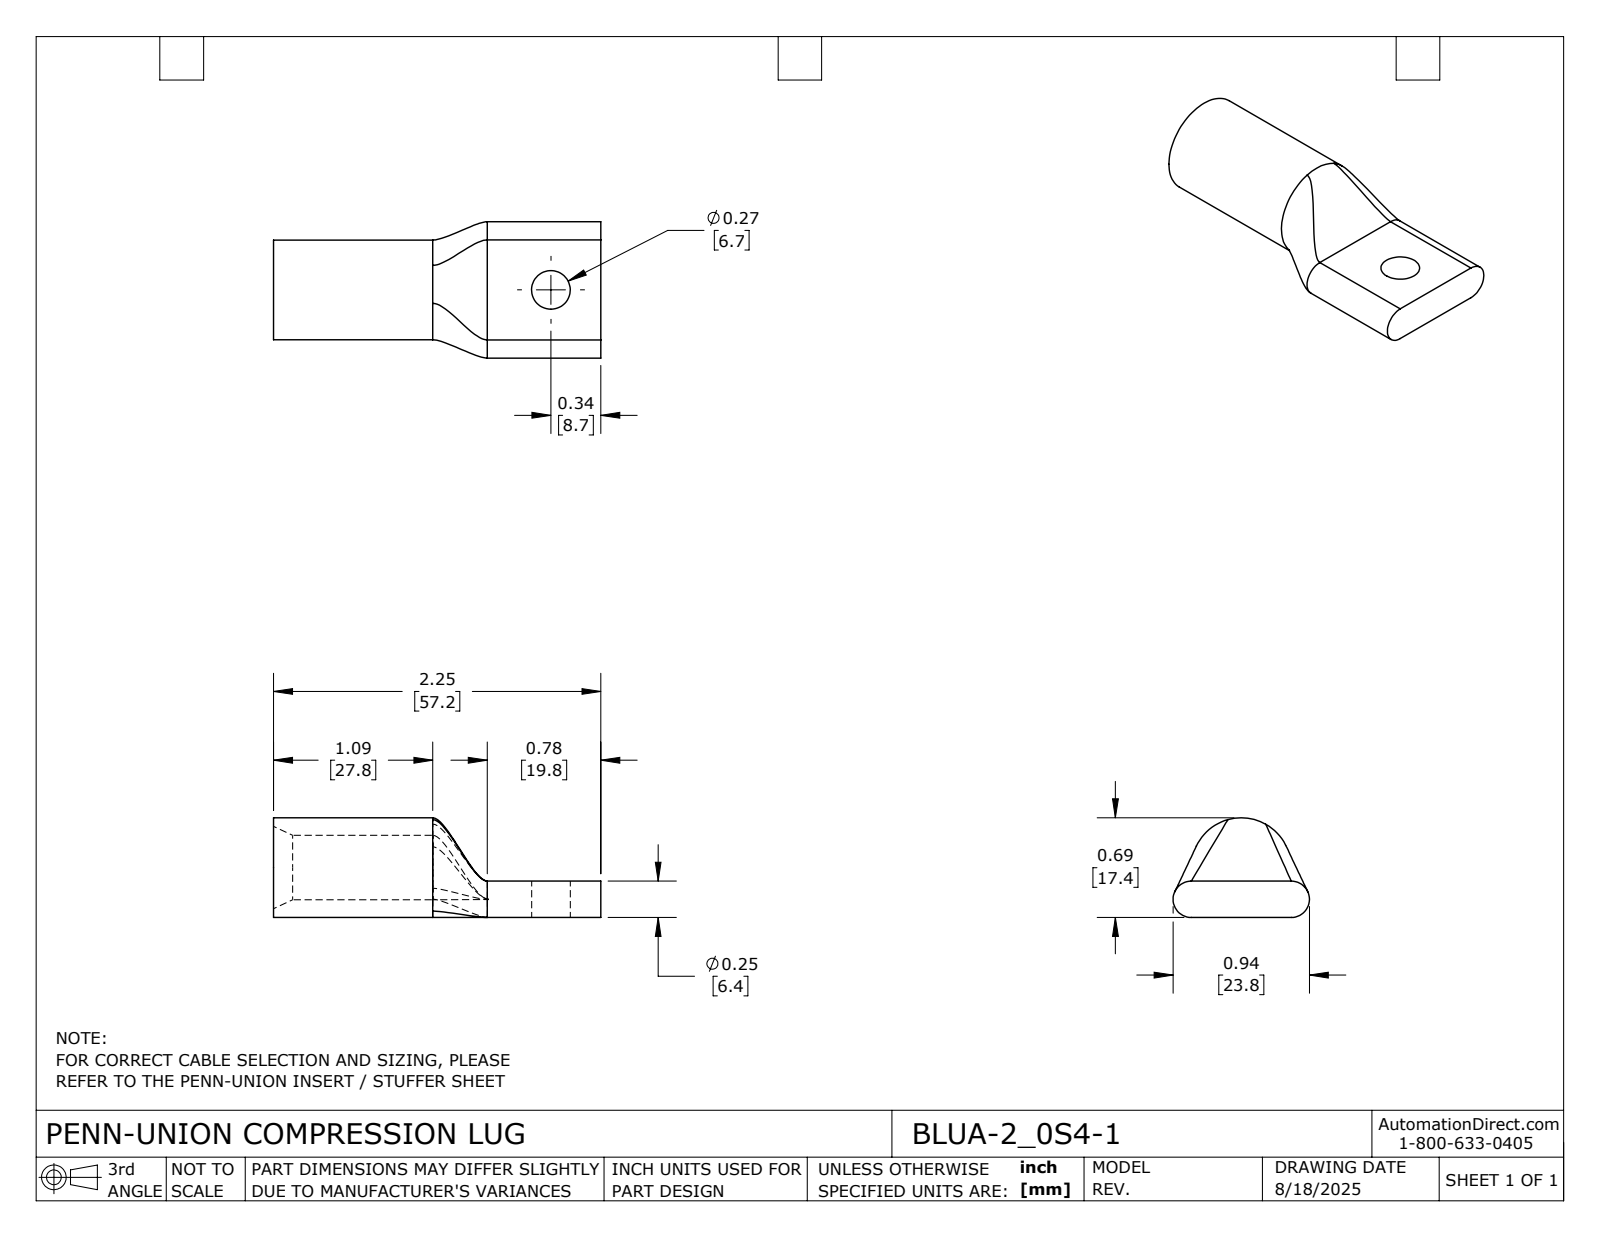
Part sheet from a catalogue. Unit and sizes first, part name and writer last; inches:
Units: inches
Overall size (bounding box): 2.25 × 0.938 × 0.685
Round holes (diameter × count): ⌀0.266 ×1, ⌀0.443 ×1
Round bosses / shafts (diameter × count): ⌀0.685 ×1
Partial cylindrical surfaces — rounded edges, fillets, slot ends (radius × count): R0.125 ×2
Main face-to-face distances: 0.25, 2.25, 1.469, 0.781
Volume: 0.468 in³ · Surface area: 7.605 in²
Bodies: 1 solid, 24 faces (5 planar, 9 cylindrical, 10 other)
Part name (STEP PRODUCT): BLUA-2_0S4-1
STEP written by: SolidWorks 2024 (CONFIG_CONTROL_DESIGN)
